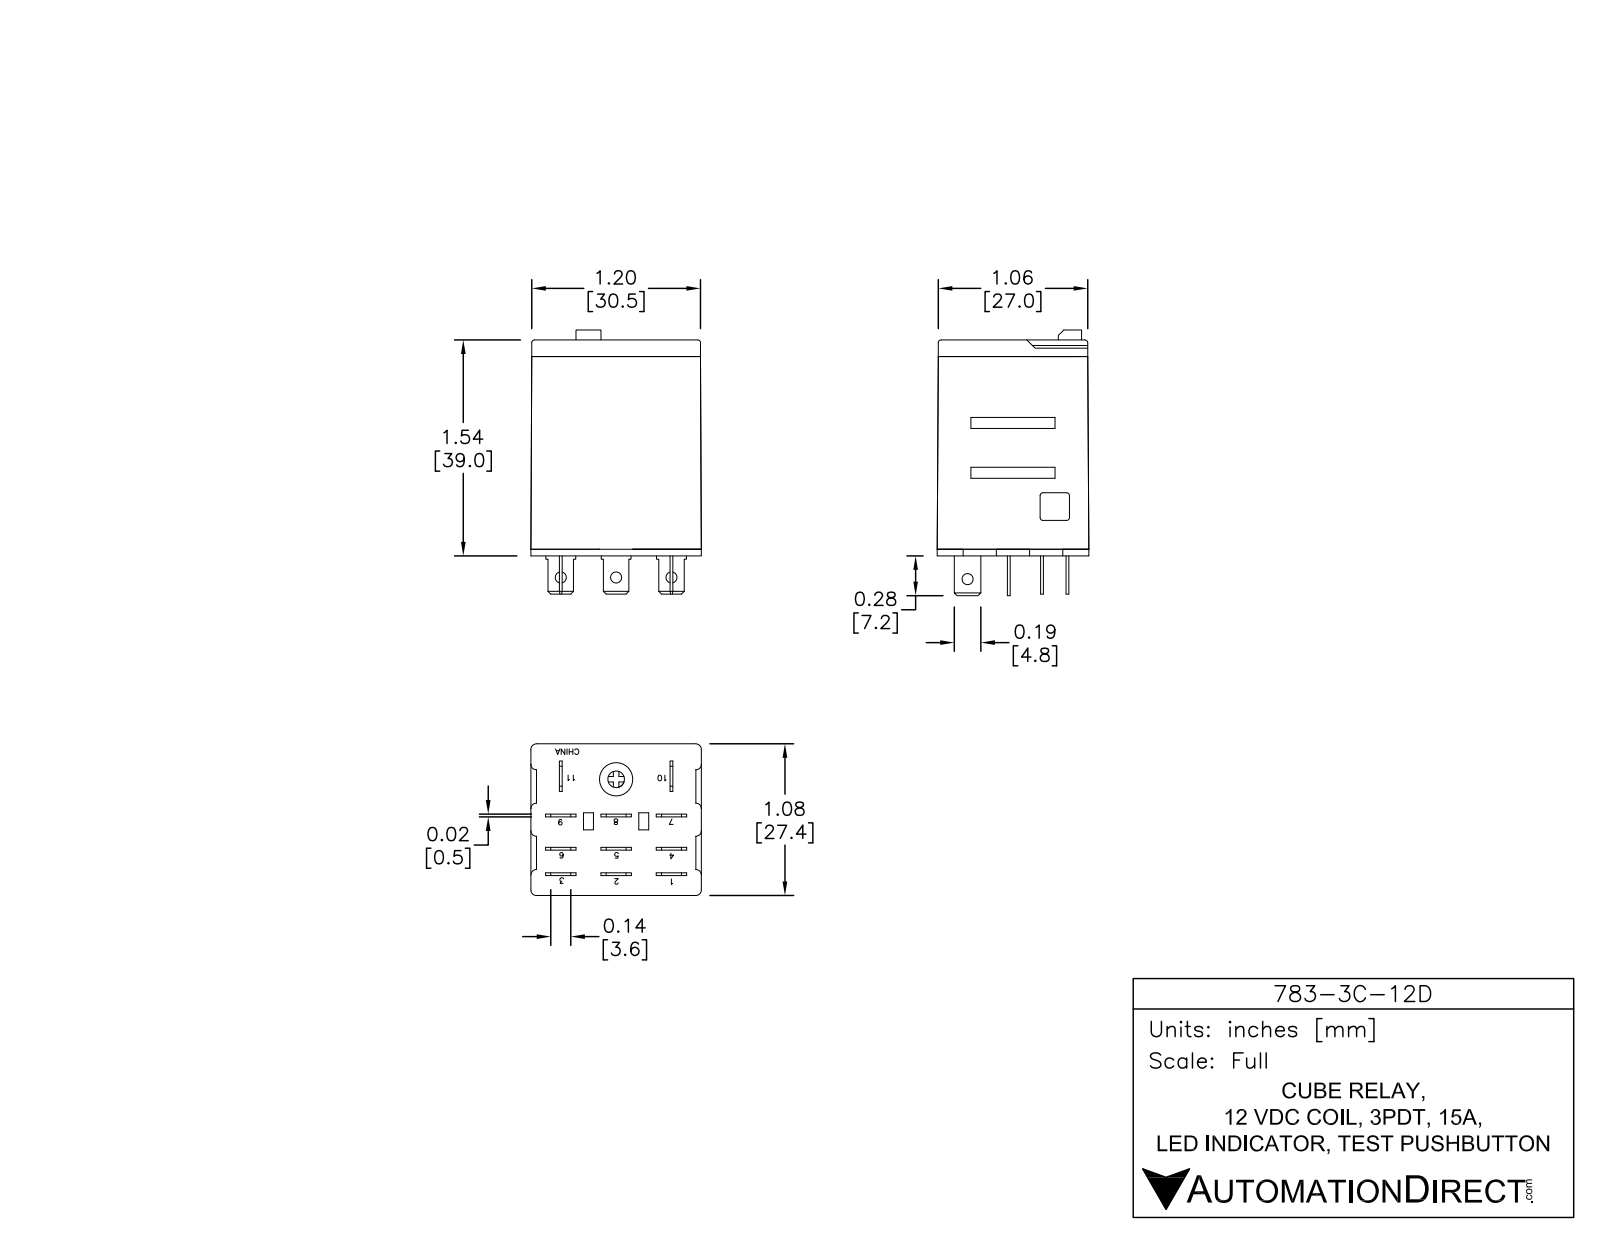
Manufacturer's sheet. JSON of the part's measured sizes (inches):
{"part_name": "783-3C-12D", "step_written_by": "SolidWorks 2021 (CONFIG_CONTROL_DESIGN)", "units": "inches", "bodies": {"solids": 1, "faces": 164, "planar": 137, "cylindrical": 27, "other": 0}, "overall_size": [1.86, 1.2, 1.1], "volume_in3": 2.053, "surface_area_in2": 11.06, "round_holes": [[0.11, 4], [0.15, 1]], "round_bosses_or_shafts": [[0.07, 1]], "partial_cylinders_radius": [[0.88, 1]], "face_to_face_distances": [1.6, 0.02, 0.21, 0.23, 0.04, 0.4, 1.56, 0.19, 0.17, 0.19], "hole_center_spacings": [0.39, 0.78]}
